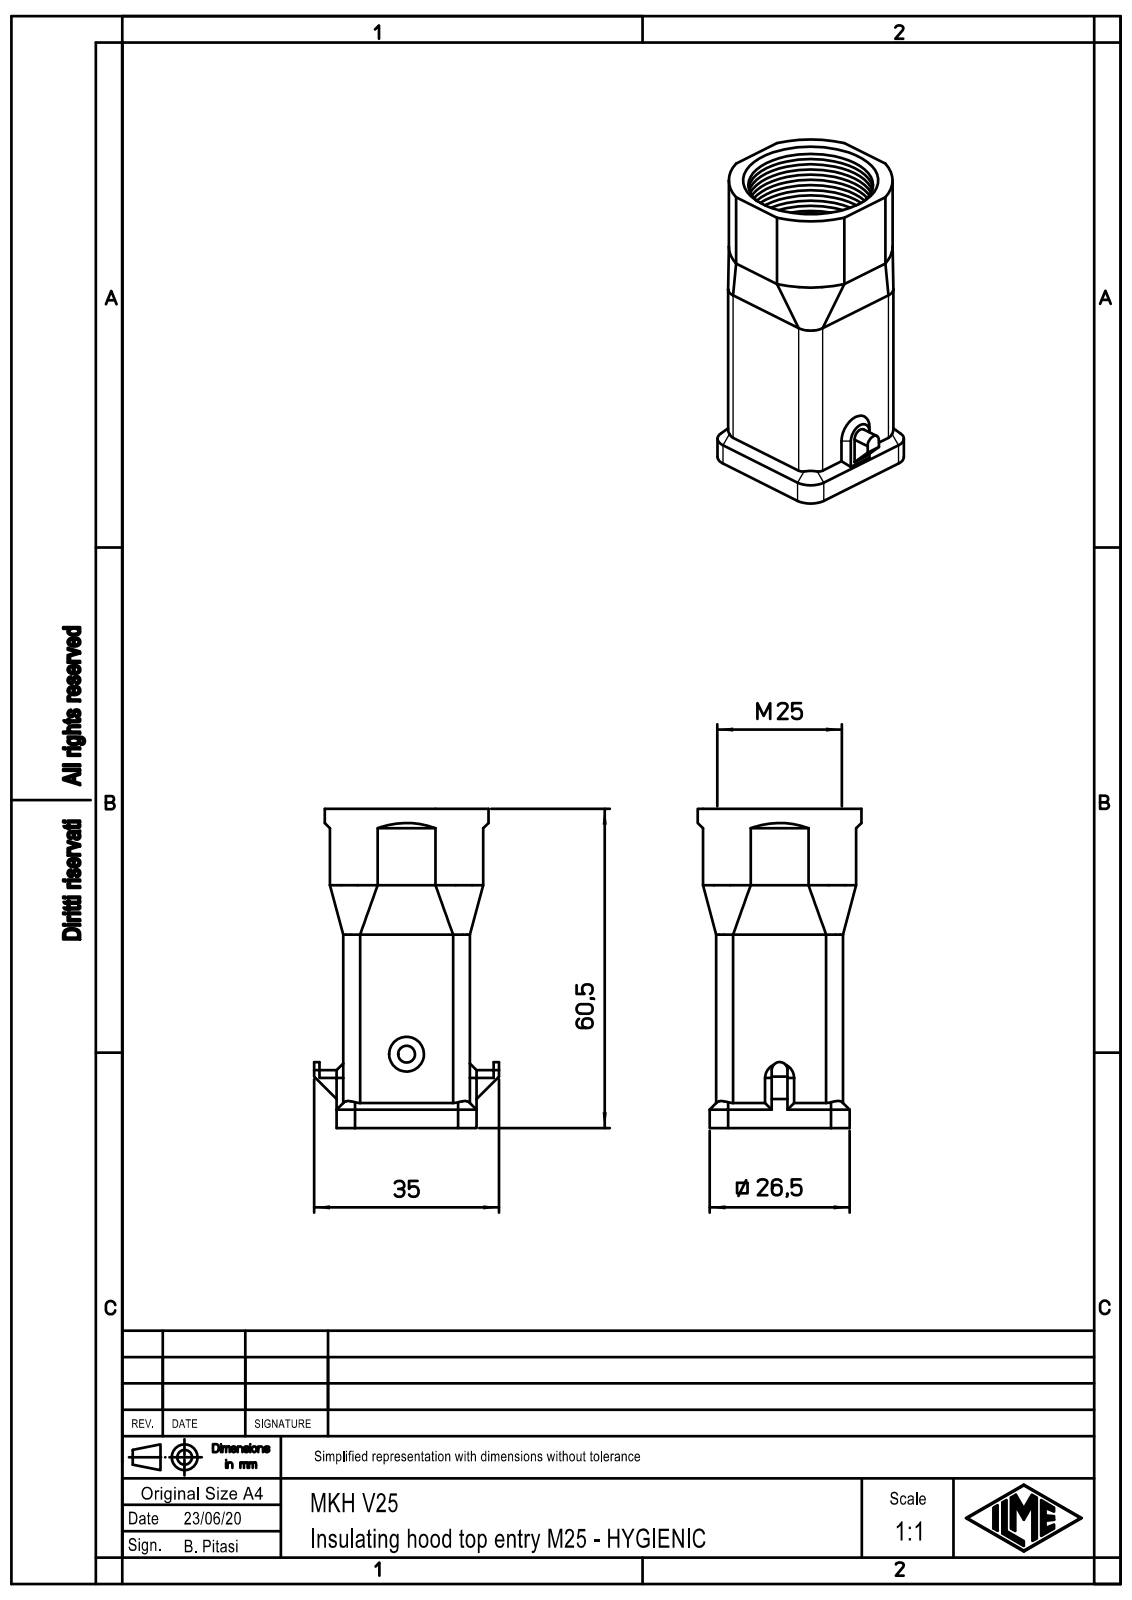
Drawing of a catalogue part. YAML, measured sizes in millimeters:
part_name: "MKH V25; MKH V25.stp"
step_written_by: "Creo Elements/Direct Modeling 20.1B 02-Apr-2019 (C) Parametric Technology GmbH (AUTOMOTIVE_DESIGN)"
units: millimeters
bodies: {solids: 1, faces: 283, planar: 216, cylindrical: 52, other: 15}
overall_size: [60.5, 33.5, 29.3]
volume: 10753
surface_area: 11628
round_holes:
  - {diameter: 3.2, count: 1}
  - {diameter: 7, count: 1}
  - {diameter: 20, count: 1}
  - {diameter: 23.6, count: 1}
partial_cylinders:
  - {radius: 0.2, count: 11}
  - {radius: 2, count: 8}
  - {radius: 3.2, count: 4}
  - {radius: 3.5, count: 4}
  - {radius: 0.1, count: 3}
  - {radius: 0.16, count: 2}
  - {radius: 1.75, count: 2}
  - {radius: 2.5, count: 2}
face_to_face_distances: [1.2, 22.8, 21.6, 24, 1.5, 26.5, 2.5, 24.3, 3.7, 25.3]
